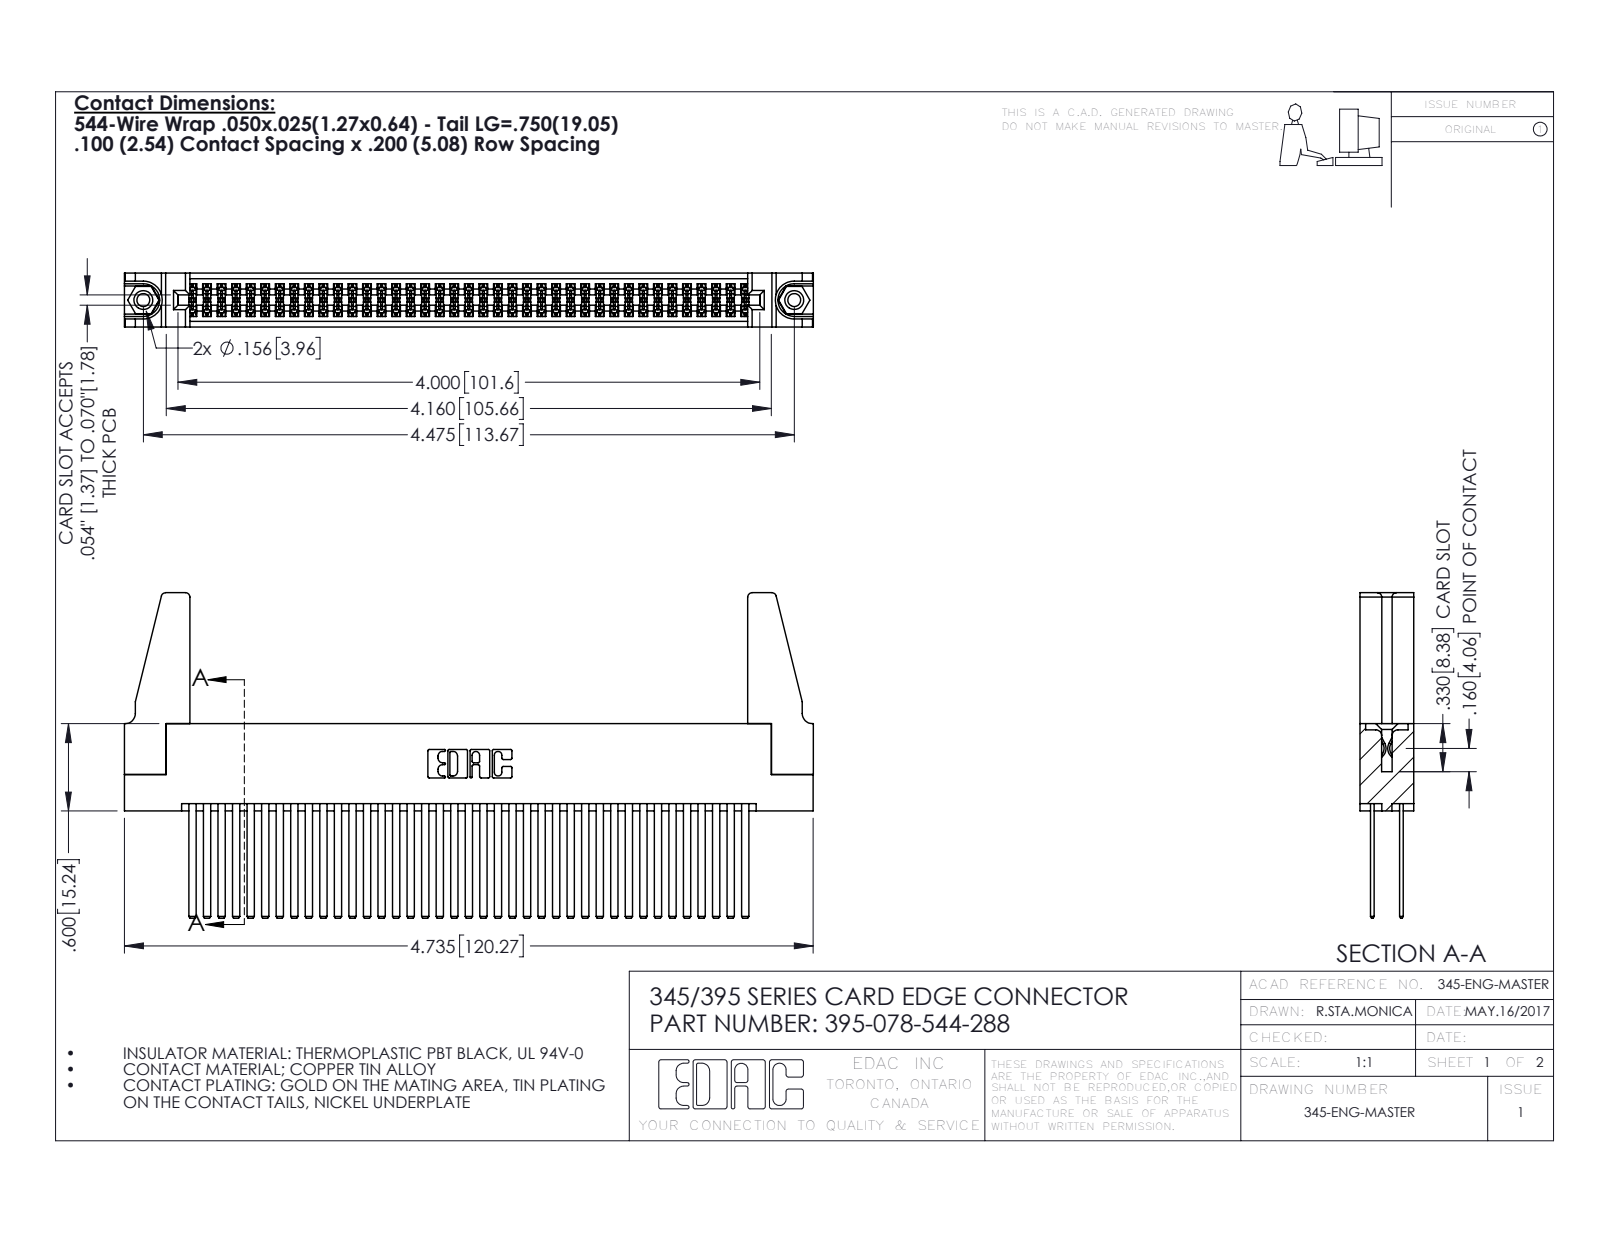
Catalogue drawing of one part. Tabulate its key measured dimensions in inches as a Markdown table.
| quantity | value |
| --- | --- |
| part name | 345-292-001_345-293-144; 345 Part_Flush Mounting Lugs - 0.156 Dia-TH; 345-250-001_345-250-001-102; 395-078-544-288 (+1 more) |
| STEP written by | SolidWorks 2016 (CONFIG_CONTROL_DESIGN) |
| units | inches |
| bodies | 83 solids, 3682 faces (2414 planar, 1252 cylindrical, 16 other) |
| overall size | 4.736 × 2.237 × 0.37 |
| volume | 0.977 in³ |
| surface area | 38.93 in² |
| round holes (diameter × count) | 0.089 × 2, 0.125 × 2, 0.156 × 2, 0.064 × 1 |
| round bosses / shafts (diameter × count) | 0.155 × 2 |
| partial cylindrical surfaces (radius × count) | 0.006 × 117, 0.01 × 22, 0.03 × 8, 0.007 × 6, 0.031 × 6, 0.026 × 3, 0.014 × 2, 0.019 × 2 |
| main face-to-face distances | 0.072, 0.298, 0.2, 0.098, 0.272, 0.025, 0.225, 0.37, 0.175, 0.149 |
| hole center spacings | 0.27, 4.239, 4.475 |
